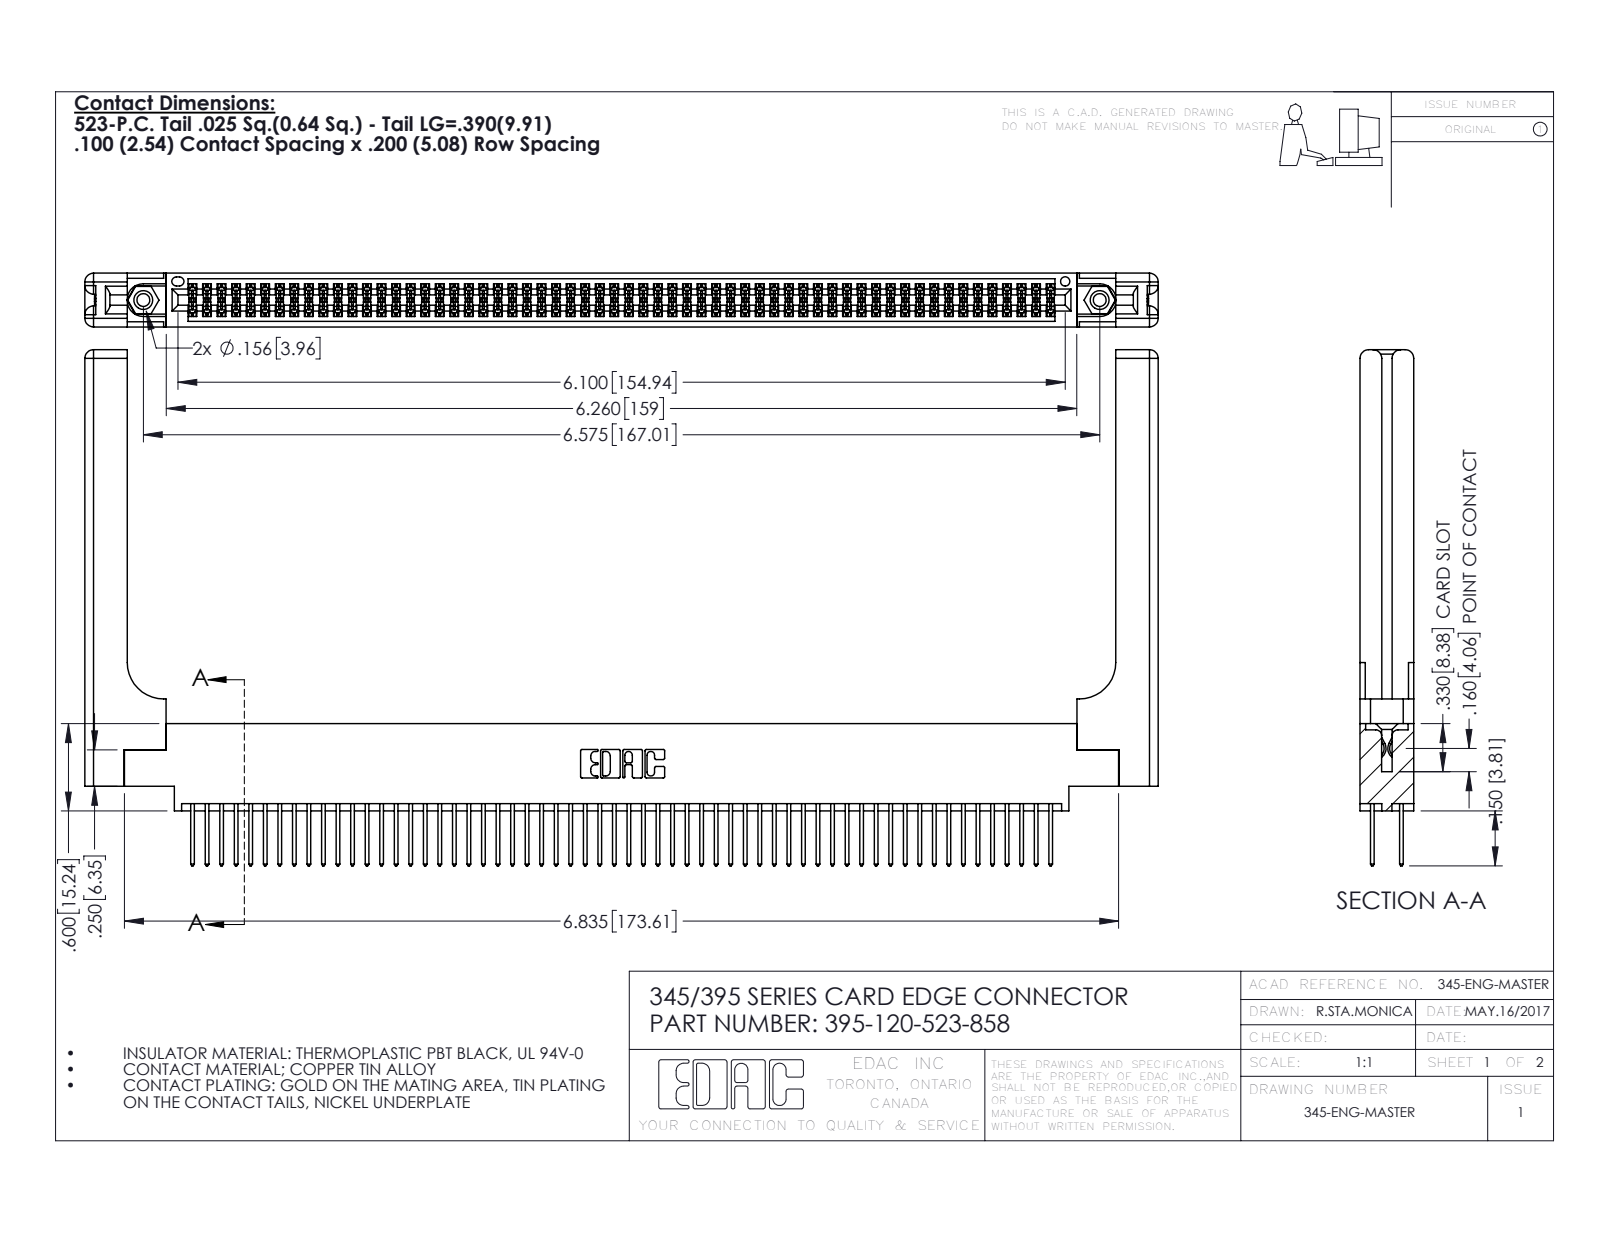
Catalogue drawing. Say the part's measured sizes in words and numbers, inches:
The part is named "345-292-001_345-293-123; 345-220-058_345-220-058; 345-250-001_345-250-001-102; 395-120-523-858 (+1 more)". Its 3-D file was written by "SolidWorks 2016 (CONFIG_CONTROL_DESIGN)". It is 125 solids with 6386 faces: 4192 planar, 2134 cylindrical and 60 other. Overall it measures 7.379 by 3.547 by 0.37 inches. Its volume is 1.647 cubic inches and its surface area 52.72 square inches. Round holes: 2 of diameter 0.089, 2 of diameter 0.125, 2 of diameter 0.156, 1 of diameter 0.064. Round bosses or shafts: 2 of diameter 0.155. Partial cylindrical surfaces (rounded edges, fillets, slot ends): 180 of radius 0.006, 120 of radius 0.01, 22 of radius 0.01, 16 of radius 0.06, 6 of radius 0.007, 6 of radius 0.031, 3 of radius 0.026, 2 of radius 0.014. The main face-to-face distances are 0.072, 0.298, 0.37, 0.098, 0.272, 0.025, 0.2, 0.225, 0.175, 0.148. The hole center spacings are 0.27, 6.339, 6.575.
